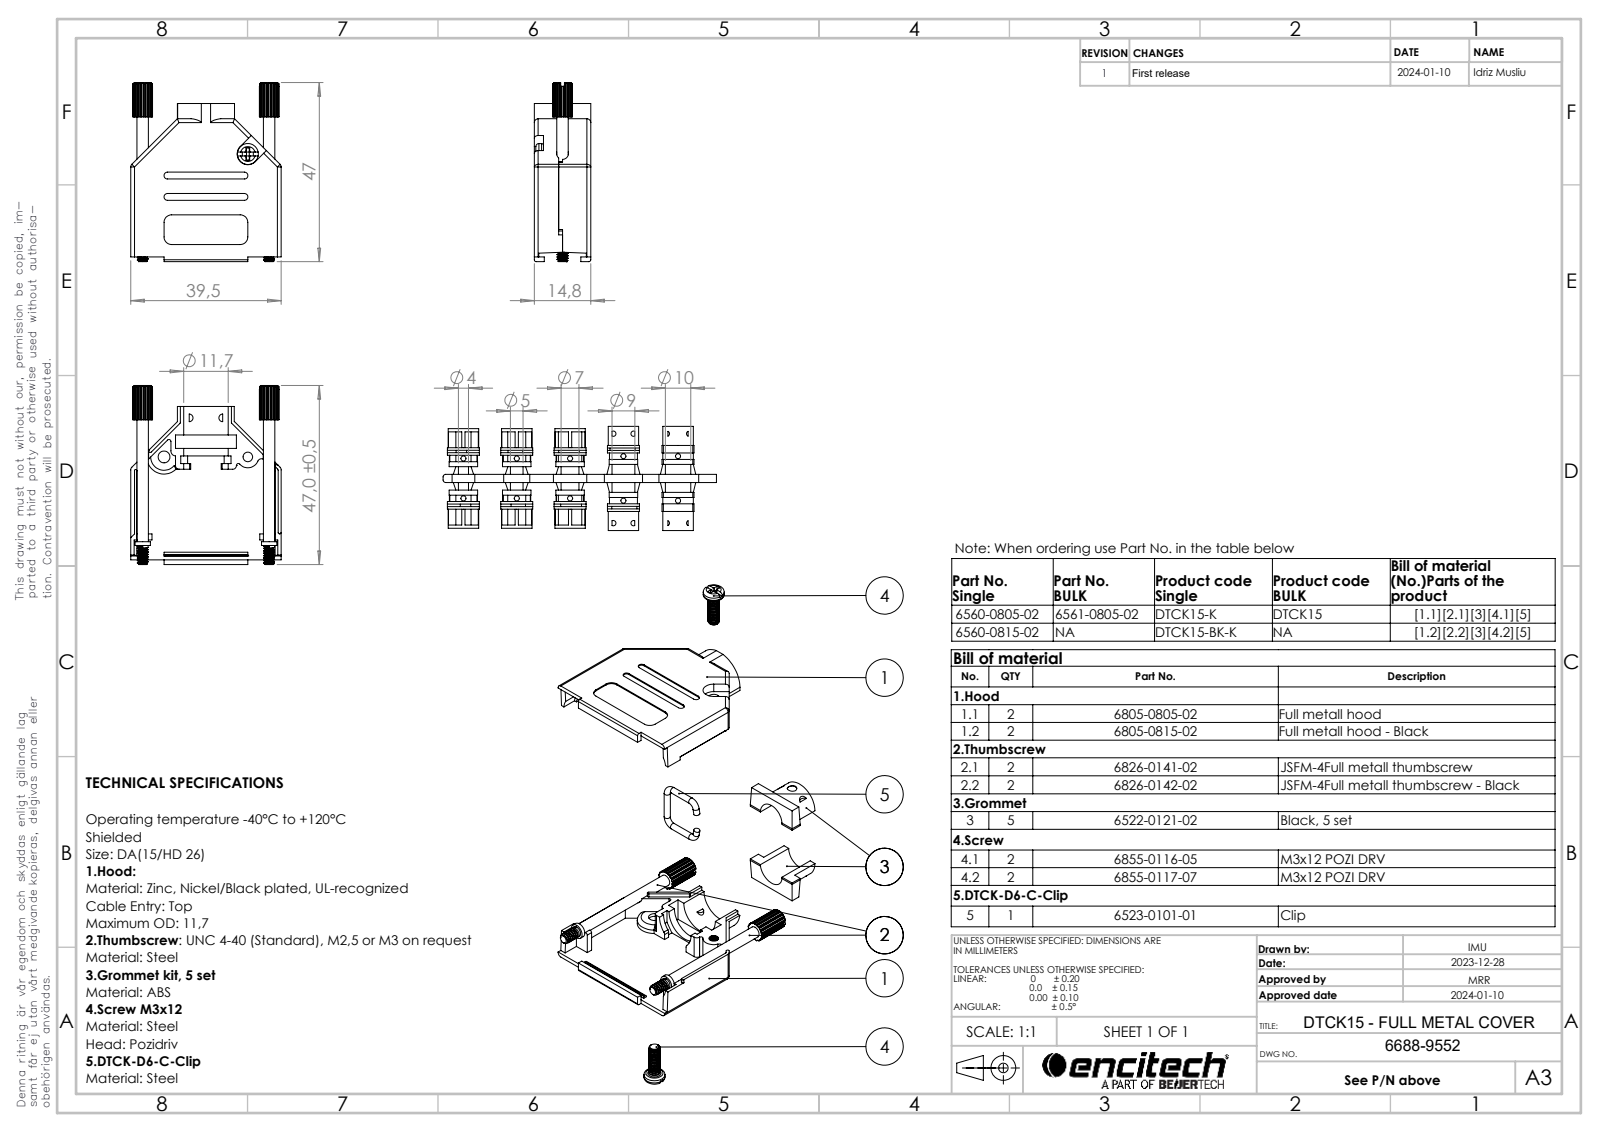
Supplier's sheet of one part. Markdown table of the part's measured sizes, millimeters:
| quantity | value |
| --- | --- |
| part name | 6688-9552; 6805-0805-02; 6826-0141-02; 6522-0121-02 (7mm) (+2 more) |
| STEP written by | SolidWorks 2021 (AUTOMOTIVE_DESIGN) |
| units | millimeters |
| bodies | 9 solids, 802 faces (384 planar, 356 cylindrical, 62 other) |
| overall size | 47 × 39.5 × 14.8 |
| volume | 7 810 mm³ |
| surface area | 12 061 mm² |
| round holes (diameter × count) | 3.1 × 4, 2.5 × 3, 8 × 1, 11.7 × 1 |
| round bosses / shafts (diameter × count) | 1.6 × 5, 3 × 4, 5.5 × 2, 4 × 2, 2.85 × 2, 15 × 1, 11.5 × 1 |
| partial cylindrical surfaces (radius × count) | 1 × 24, 0.25 × 18, 0.4 × 10, 0.5 × 10, 0.9 × 4, 2 × 4, 5 × 4, 0.35 × 2 |
| main face-to-face distances | 13.65, 1.15, 12.5, 14.8, 7.4, 6.25, 1.6, 0.85, 14.5, 7.1 |
| hole center spacings | 15.21, 16.6, 22, 33.2 |
